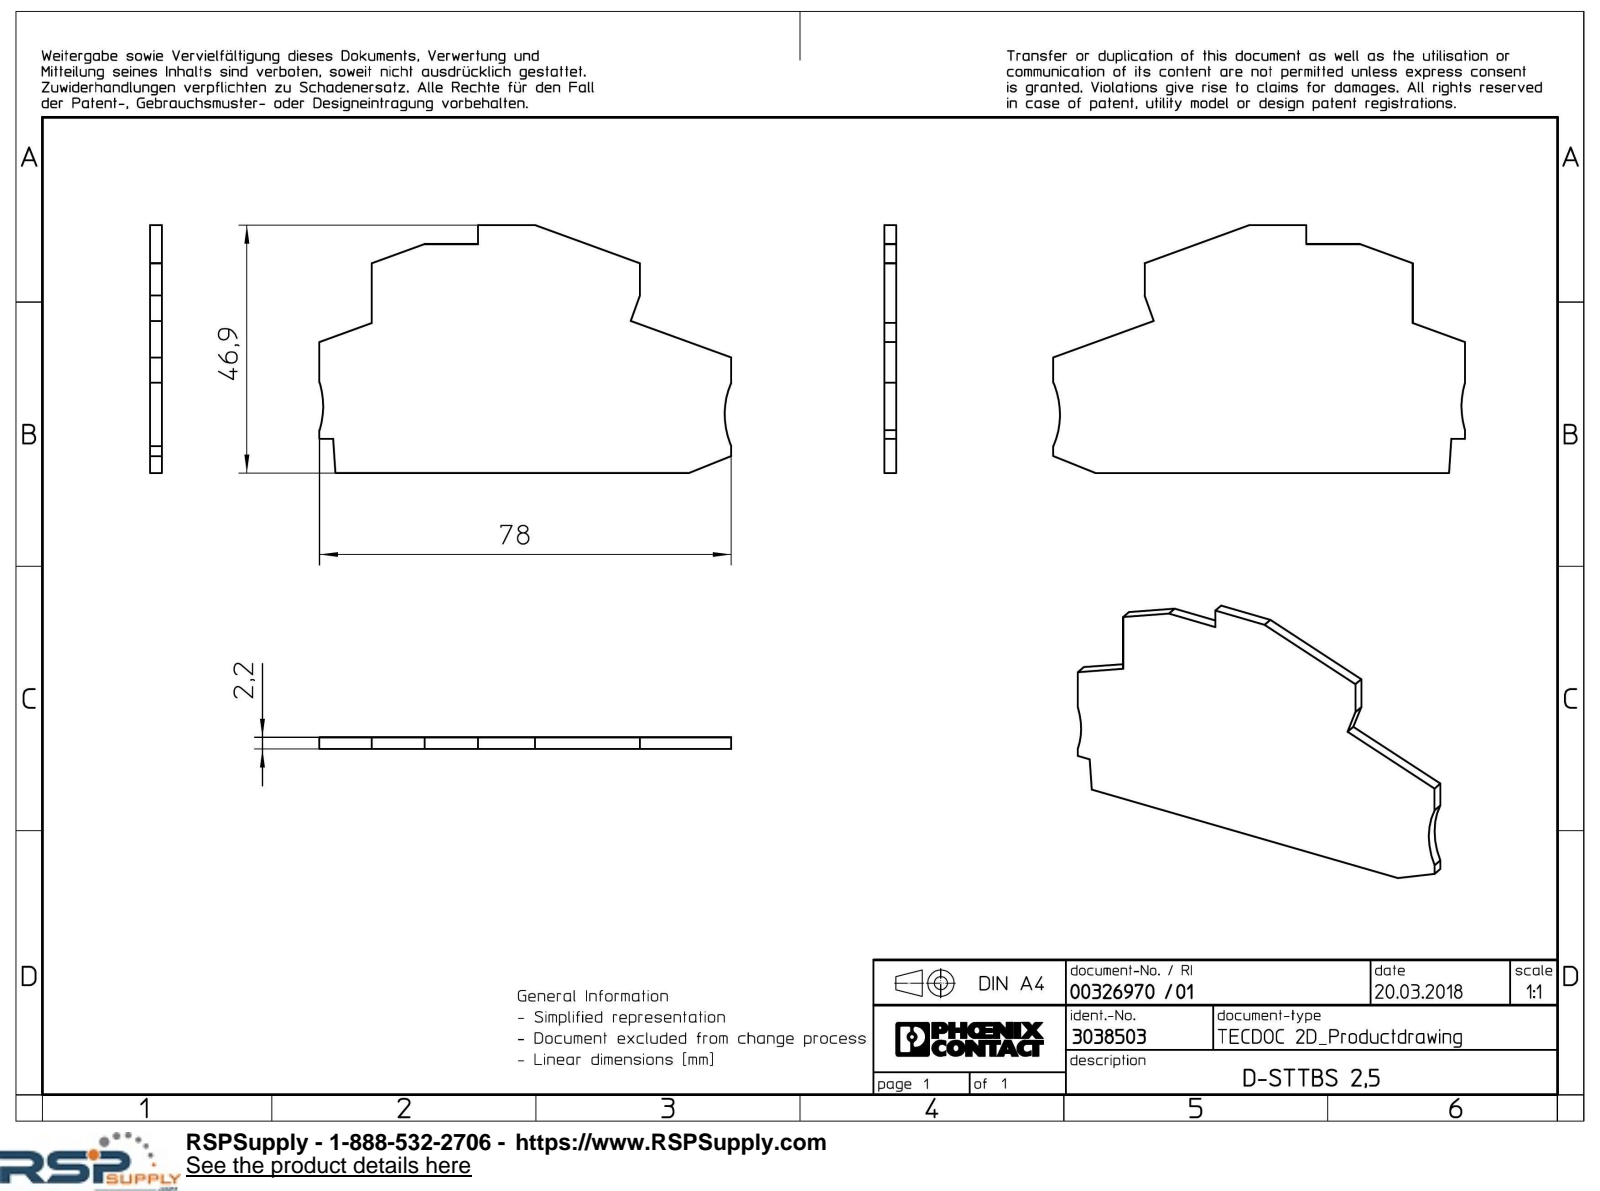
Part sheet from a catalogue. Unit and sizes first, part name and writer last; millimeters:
Units: millimetres
Overall size (bounding box): 78 × 46.91 × 2.2
Partial cylindrical surfaces — rounded edges, fillets, slot ends (radius × count): R15 ×2
Main face-to-face distances: 2.2, 10.83, 46.92, 10.6, 43.32, 3.6, 9.9, 78, 68.1, 60.7
Volume: 6 307 mm³ · Surface area: 6 243 mm²
Bodies: 1 solid, 22 faces (20 planar, 2 cylindrical, 0 other)
Part name (STEP PRODUCT): d-sttbs_25_select
STEP written by: Creo Elements/Direct Modeling 20.1A 29-Sep-2018 (C) Parametric Technology GmbH (AUTOMOTIVE_DESIGN)
